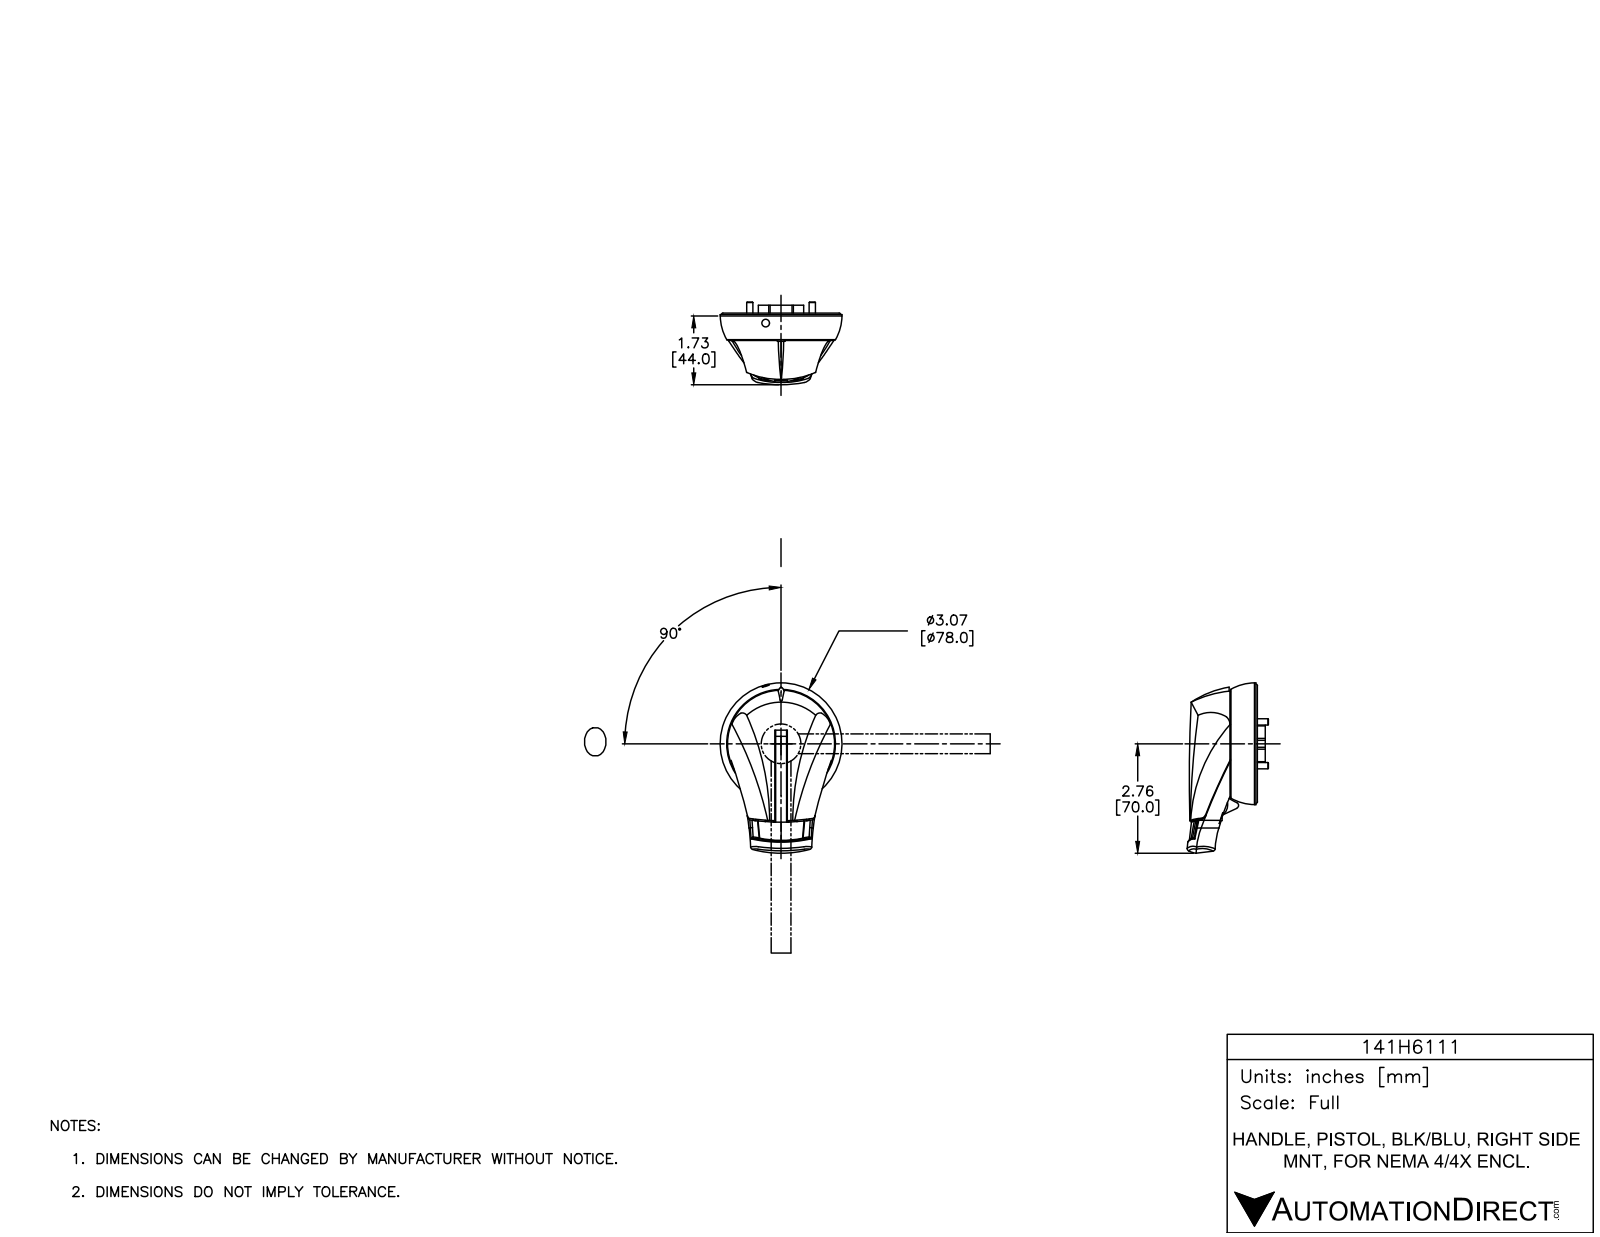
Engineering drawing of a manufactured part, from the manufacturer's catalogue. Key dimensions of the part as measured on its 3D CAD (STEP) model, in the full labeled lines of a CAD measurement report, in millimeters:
Part name (STEP PRODUCT): 141H6111
STEP written by: SolidWorks 2015 (AUTOMOTIVE_DESIGN)
Units: millimetres
Bodies: 8 solids, 1516 faces (810 planar, 548 cylindrical, 158 other)
Overall size (bounding box): 109 × 78 × 52
Volume: 126 500 mm³ · Surface area: 51 390 mm²
Round holes (diameter × count): ⌀4 ×6, ⌀8.6 ×4, ⌀10.8 ×4, ⌀0.8 ×3, ⌀4.3 ×2, ⌀9.2 ×2, ⌀3 ×1, ⌀4.8 ×1, ⌀76 ×1
Round bosses / shafts (diameter × count): ⌀0.5 ×11, ⌀8.5 ×4, ⌀8 ×4, ⌀2.3 ×3, ⌀1.8 ×3, ⌀5.8 ×2, ⌀71.6 ×1, ⌀68.6 ×1
Partial cylindrical surfaces — rounded edges, fillets, slot ends (radius × count): R0.3 ×221, R0.4 ×20, R0.9 ×20, R0.8 ×15, R1 ×4, R0.6 ×3, R138.1 ×3, R2 ×2
Main face-to-face distances: 0.6, 17.8, 18.1, 17.5, 0.9, 2.6, 7, 4.4, 6.2, 1.2
Hole centre spacings: 24.4, 7.8, 17, 27.9, 28, 30.6, 40, 47.8
